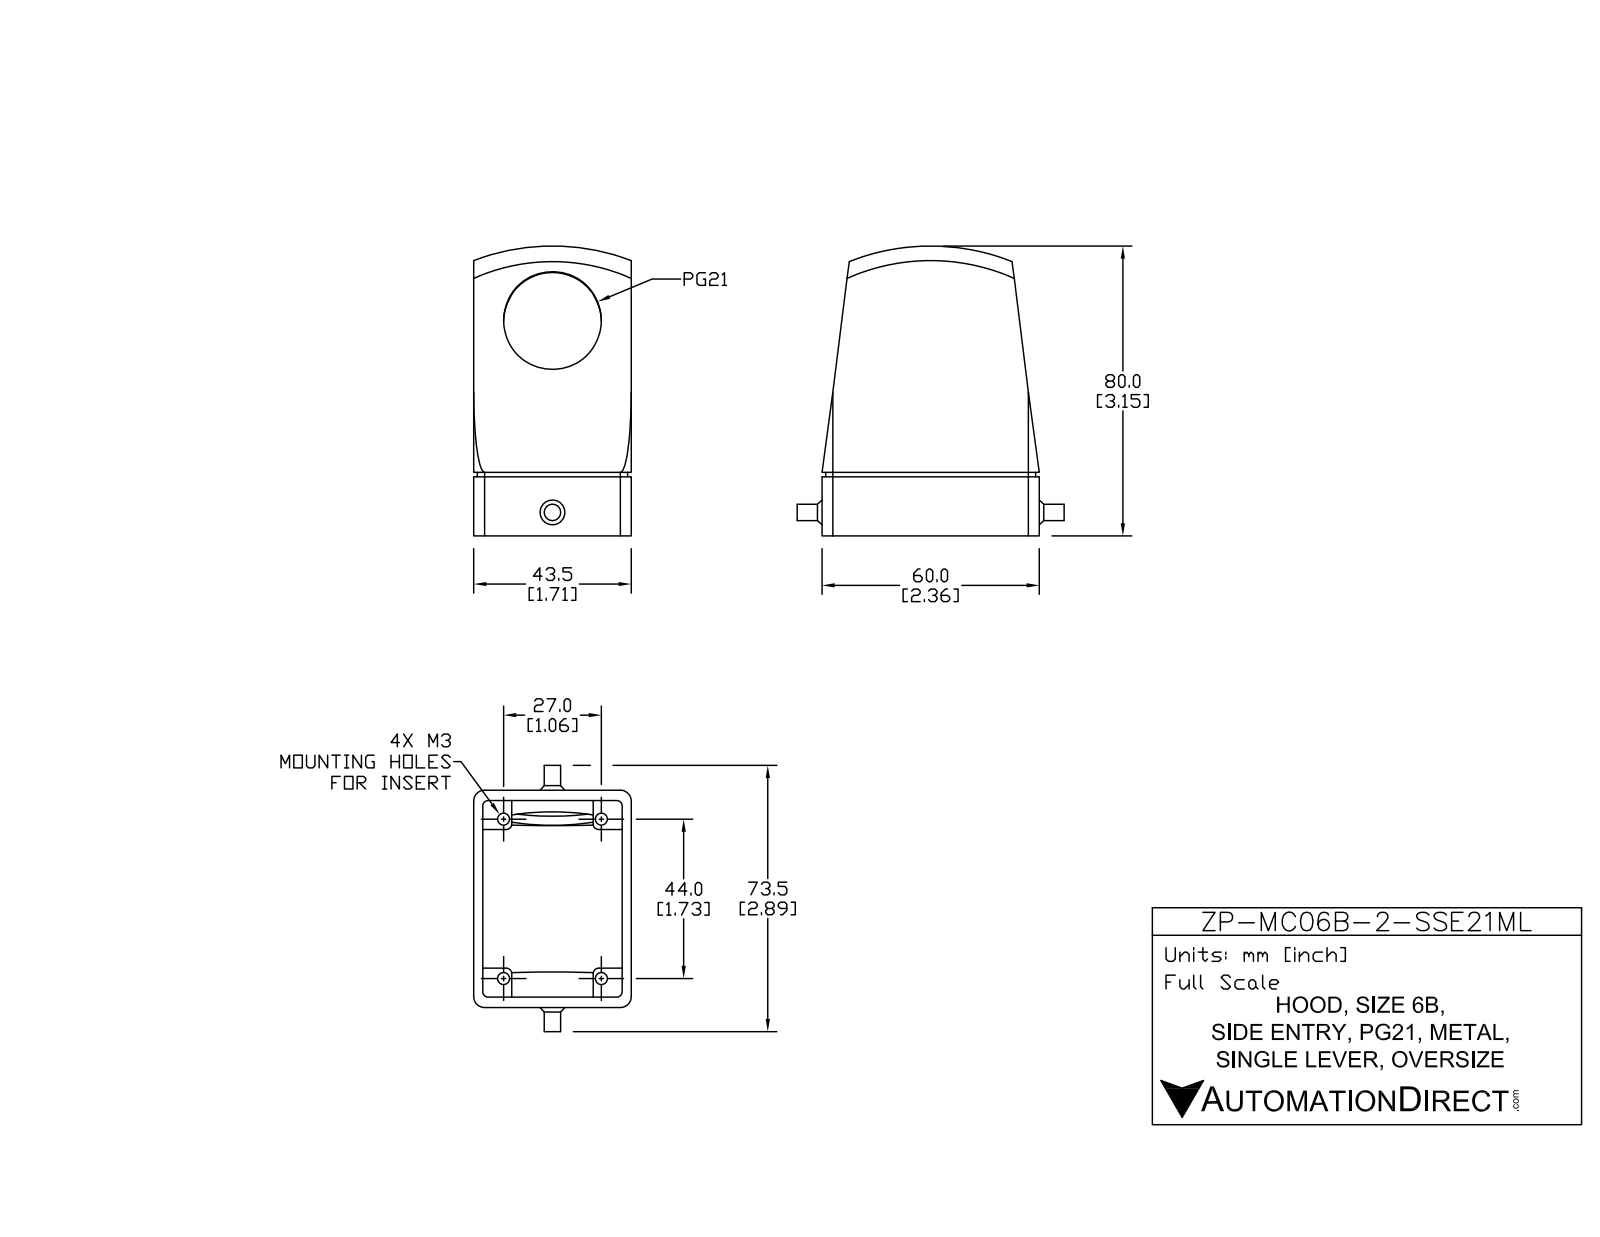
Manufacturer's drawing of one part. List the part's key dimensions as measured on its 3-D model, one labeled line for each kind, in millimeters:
Part name (STEP PRODUCT): ZP-MC06B-2-SSE21ML
STEP written by: SolidWorks 2019 (AUTOMOTIVE_DESIGN)
Units: millimetres
Bodies: 1 solid, 284 faces (91 planar, 126 cylindrical, 67 other)
Overall size (bounding box): 80 × 74.2 × 43.9
Volume: 61 420 mm³ · Surface area: 30 320 mm²
Round holes (diameter × count): ⌀2.5 ×4, ⌀3.5 ×4, ⌀23 ×1, ⌀26.8 ×1
Round bosses / shafts (diameter × count): ⌀6 ×1, ⌀4.9 ×1
Partial cylindrical surfaces — rounded edges, fillets, slot ends (radius × count): R2.5 ×6, R29.2 ×5, R1 ×4, R1.3 ×4, R1.5 ×4, R3.9 ×4, R6.7 ×4, R0.8 ×2
Main face-to-face distances: 2.8, 40.5, 43.3, 6, 3.2, 34.5, 37.3, 37.7, 11.1, 49.1
Hole centre spacings: 25.8, 27, 44, 51.6
